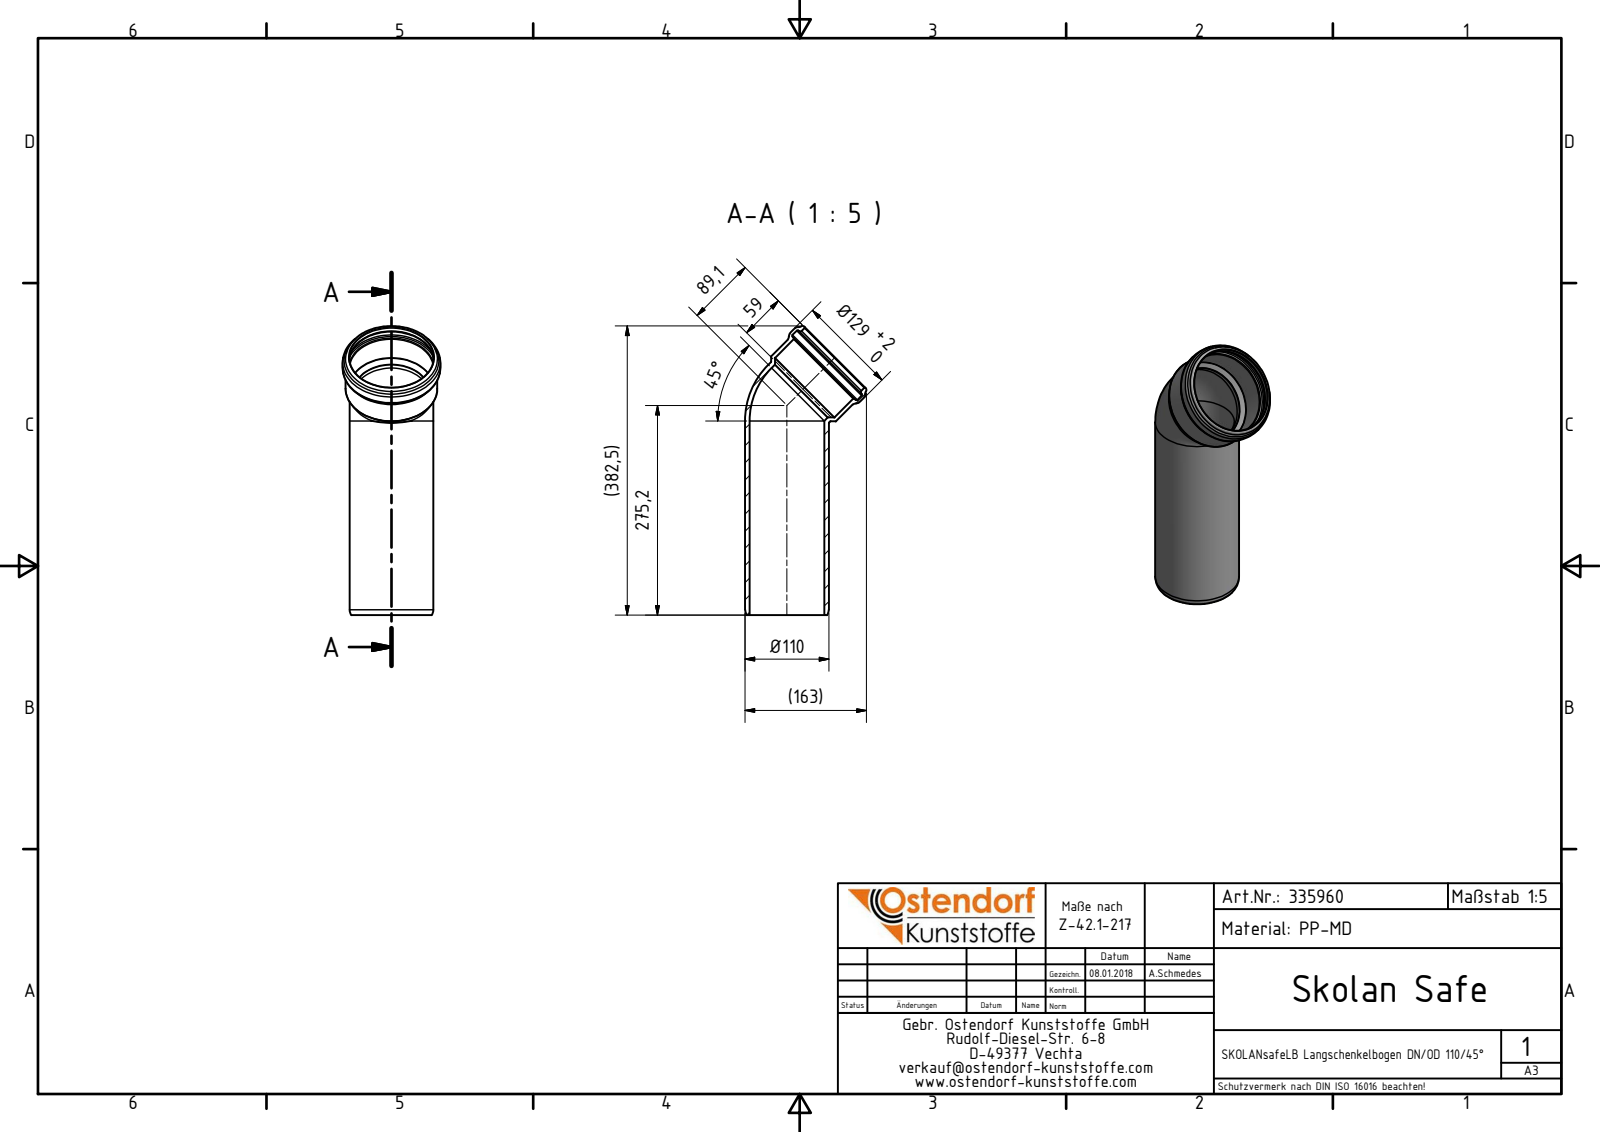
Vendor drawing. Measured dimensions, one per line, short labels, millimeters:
name: 335960 SKOLANsafeLB Langschenkelbogen DN_OD 110_45°
written by: Autodesk Inventor 2016 (AUTOMOTIVE_DESIGN)
unit: mm
bodies: 1 solid, 32 faces (1 planar, 8 cylindrical, 23 other)
size: 379.42 × 159.2 × 129
volume: 697 372 mm³; area: 249 303 mm²
holes: 2× ⌀98, 1× ⌀110.4, 1× ⌀110.7, 1× ⌀120.6
bosses: 2× ⌀110, 1× ⌀120.4
